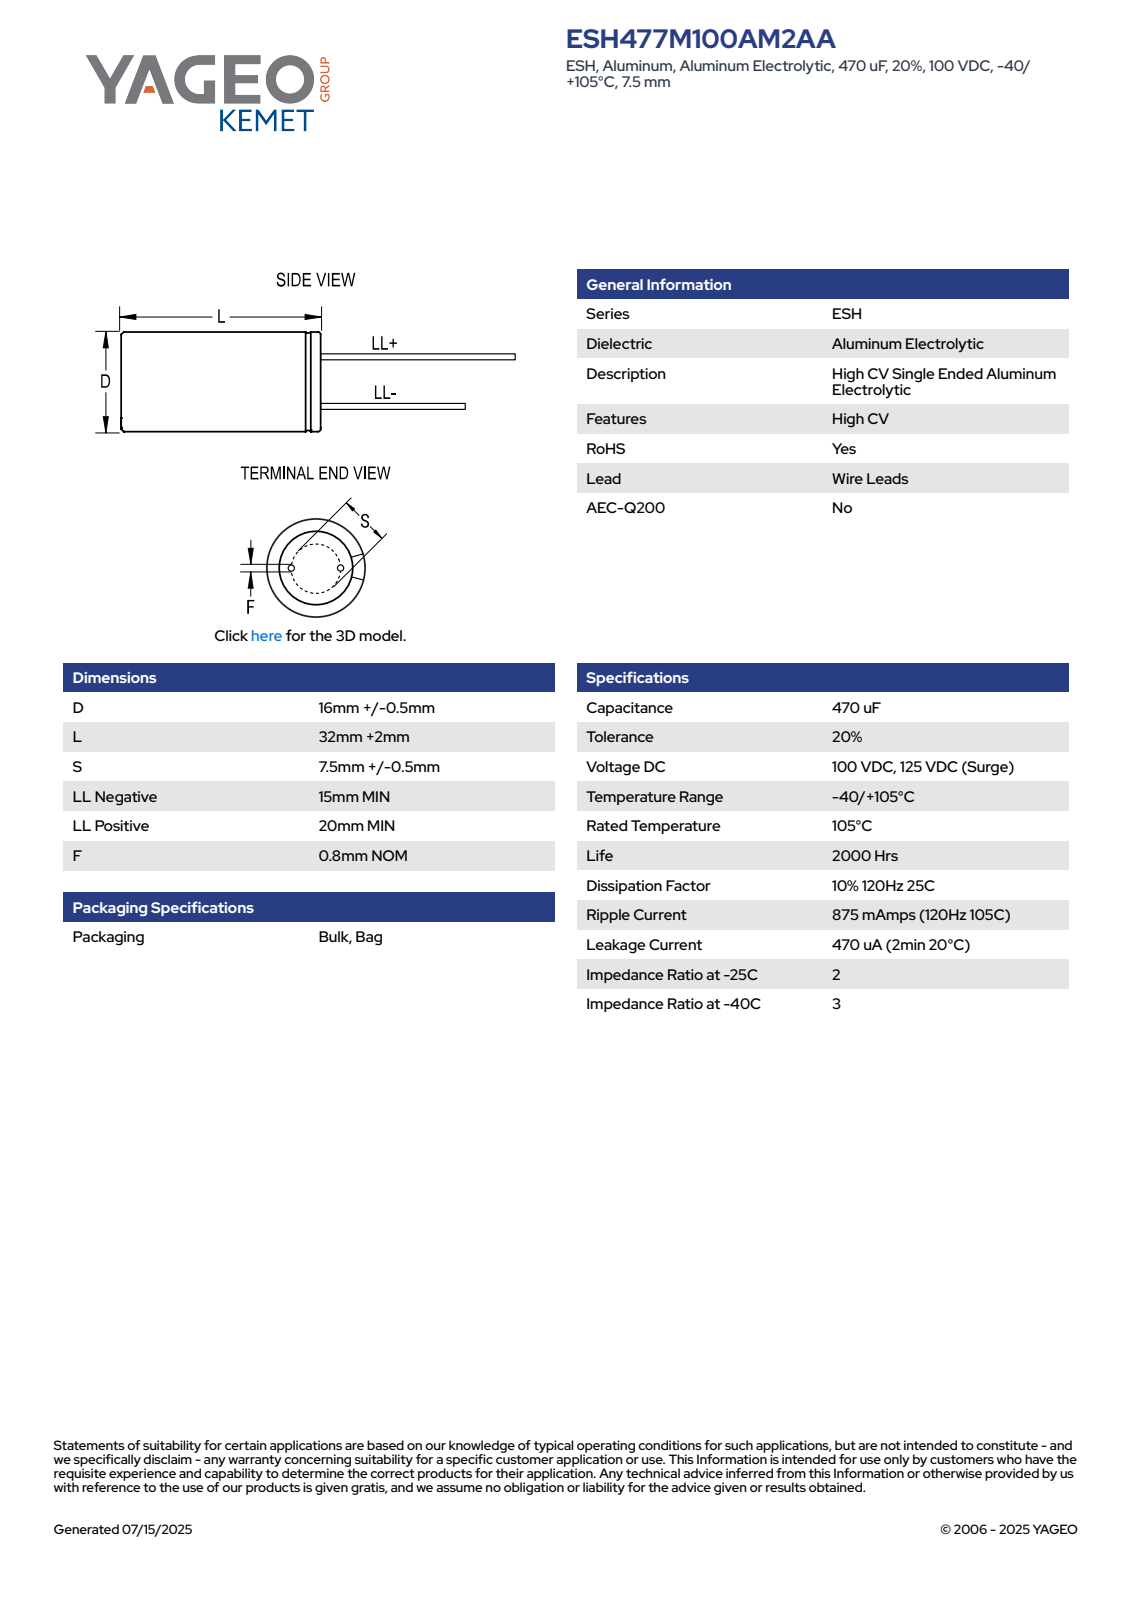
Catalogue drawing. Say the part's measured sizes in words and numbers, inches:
The part is named "CAR_KLP_16X32_D16.5L34S7.5F0.8". Its 3-D file was written by "SolidWorks 2014 (AUTOMOTIVE_DESIGN)". It is 4 solids with 75 faces: 61 planar, 8 cylindrical and 6 other. Overall it measures 2.126 by 0.65 by 0.65 inches. Its volume is 0.442 cubic inches and its surface area 3.629 square inches. Round bosses or shafts: 2 of diameter 0.031, 1 of diameter 0.65. The main face-to-face distances are 1.339, 1.339, 0.197, 1.93, 2.126, 1.929, 2.126, 0.591, 0.787, 0.087.
